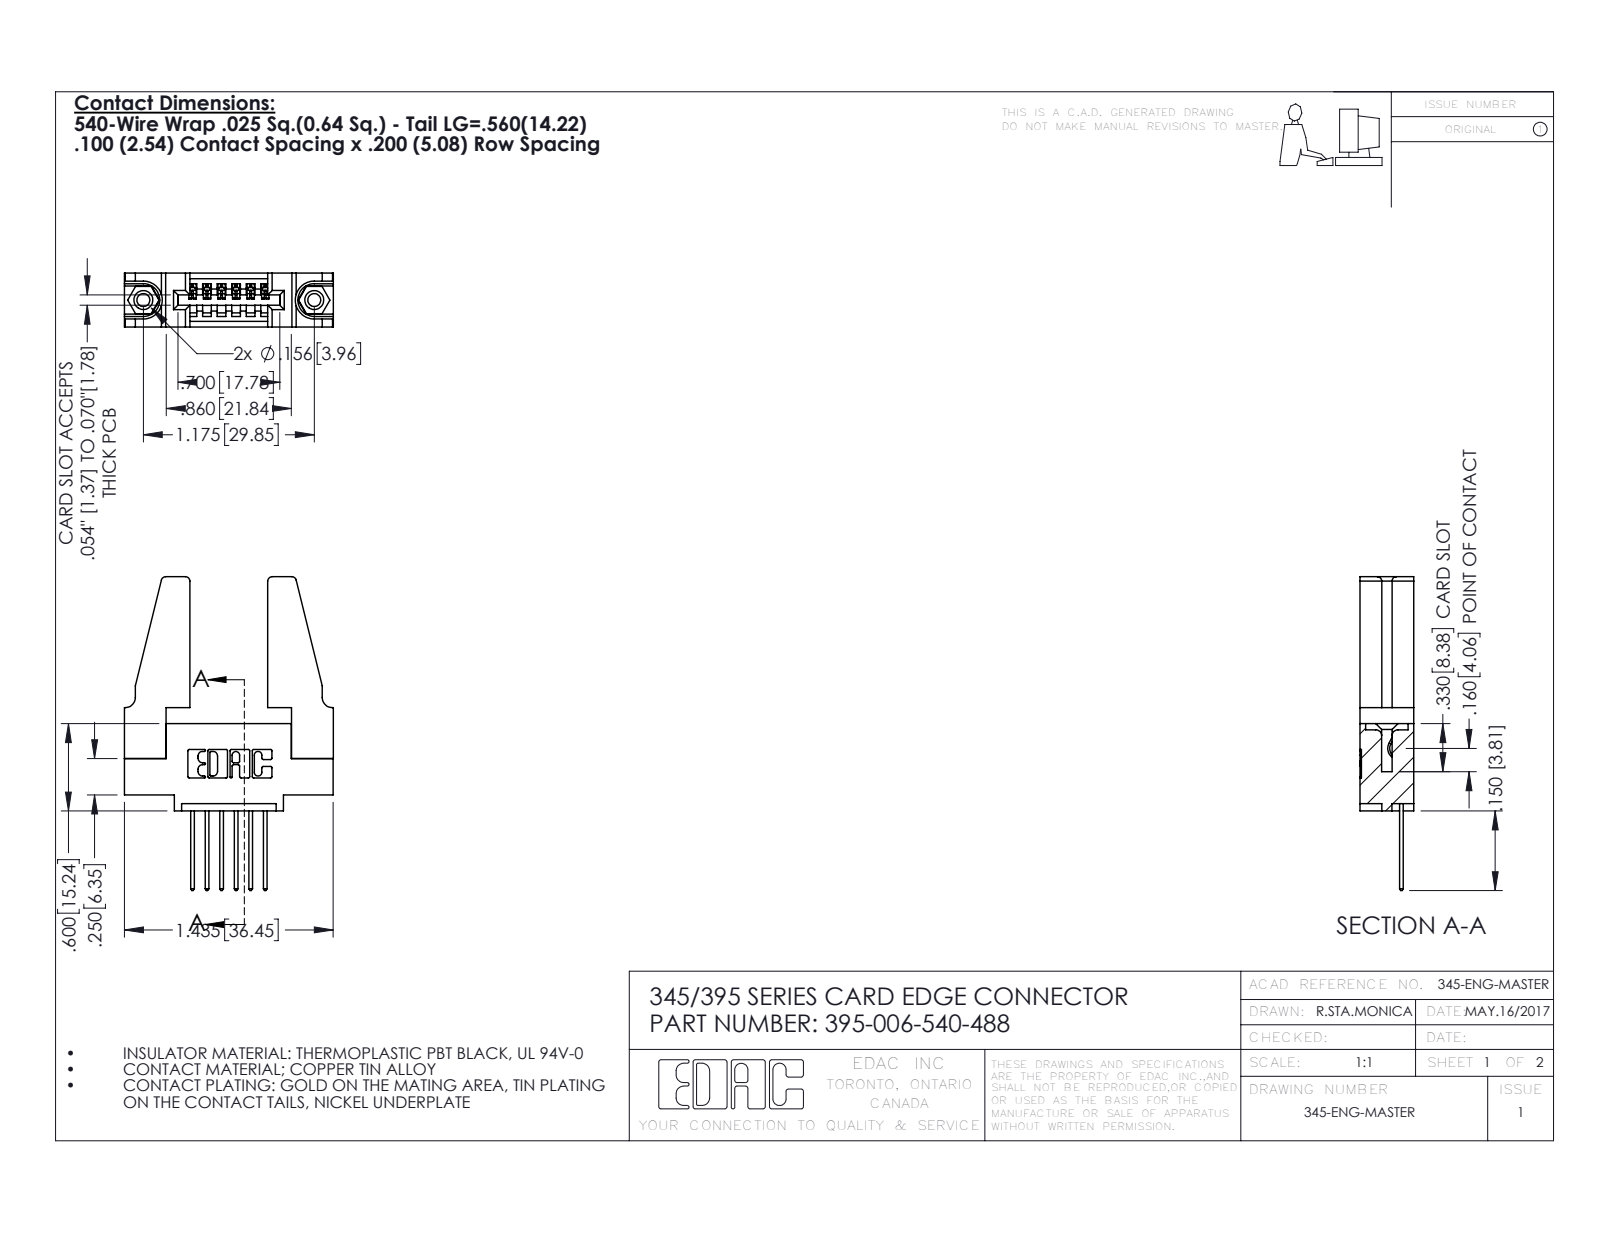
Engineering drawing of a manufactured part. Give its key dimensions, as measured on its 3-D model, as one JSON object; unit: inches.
{"part_name": "345-220-078_345-220-088; 345-250-001_345-250-001-102; 345 Part_0.110 Offset - 0.156 Dia-TH; 345-292-001_345-293-140 (+1 more)", "step_written_by": "SolidWorks 2016 (CONFIG_CONTROL_DESIGN)", "units": "inches", "bodies": {"solids": 11, "faces": 602, "planar": 396, "cylindrical": 190, "other": 16}, "overall_size": [2.157, 1.436, 0.37], "volume_in3": 0.388, "surface_area_in2": 10.7, "round_holes": [[0.089, 2], [0.125, 2], [0.156, 2], [0.064, 1]], "round_bosses_or_shafts": [[0.155, 2]], "partial_cylinders_radius": [[0.01, 22], [0.006, 12], [0.01, 12], [0.03, 8], [0.007, 6], [0.031, 6], [0.026, 3], [0.031, 2]], "face_to_face_distances": [0.37, 0.072, 0.298, 0.2, 0.098, 0.272, 0.025, 0.15, 0.148, 0.22], "hole_center_spacings": [0.27, 0.946, 1.175]}
